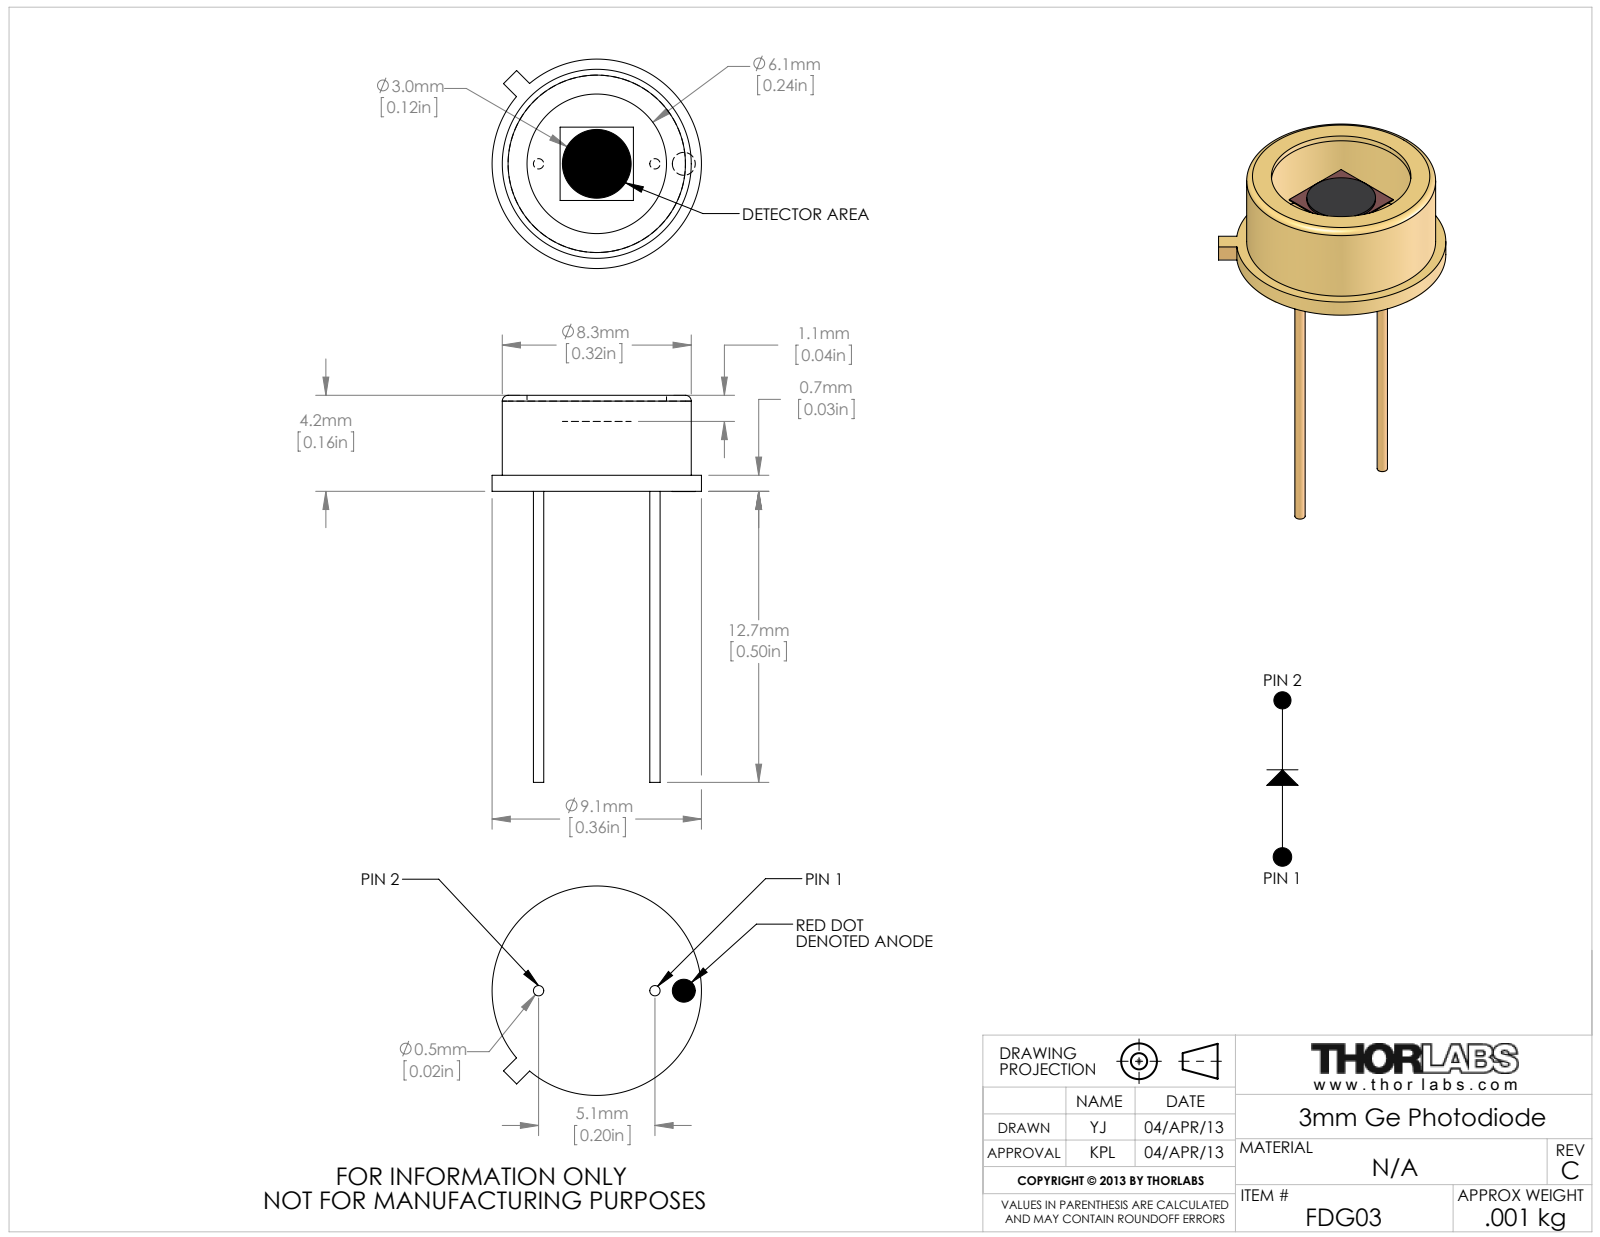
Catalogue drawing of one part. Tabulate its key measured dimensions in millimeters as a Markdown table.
| quantity | value |
| --- | --- |
| part name | 13846-E0W |
| STEP written by | SolidWorks 2012 (AUTOMOTIVE_DESIGN) |
| units | millimeters |
| bodies | 2 solids, 37 faces (18 planar, 17 cylindrical, 2 other) |
| overall size | 16.89 × 9.14 × 9.14 |
| volume | 66 mm³ |
| surface area | 425 mm² |
| round holes (diameter × count) | 6.09 × 1, 7.74 × 1 |
| round bosses / shafts (diameter × count) | 0.45 × 2, 9.14 × 1, 8.25 × 1, 3 × 1, 1 × 1 |
| main face-to-face distances | 0.45, 3.49, 3.94, 4.19, 3.74, 0.7, 3.24, 2.9, 2.45, 2.2 |
